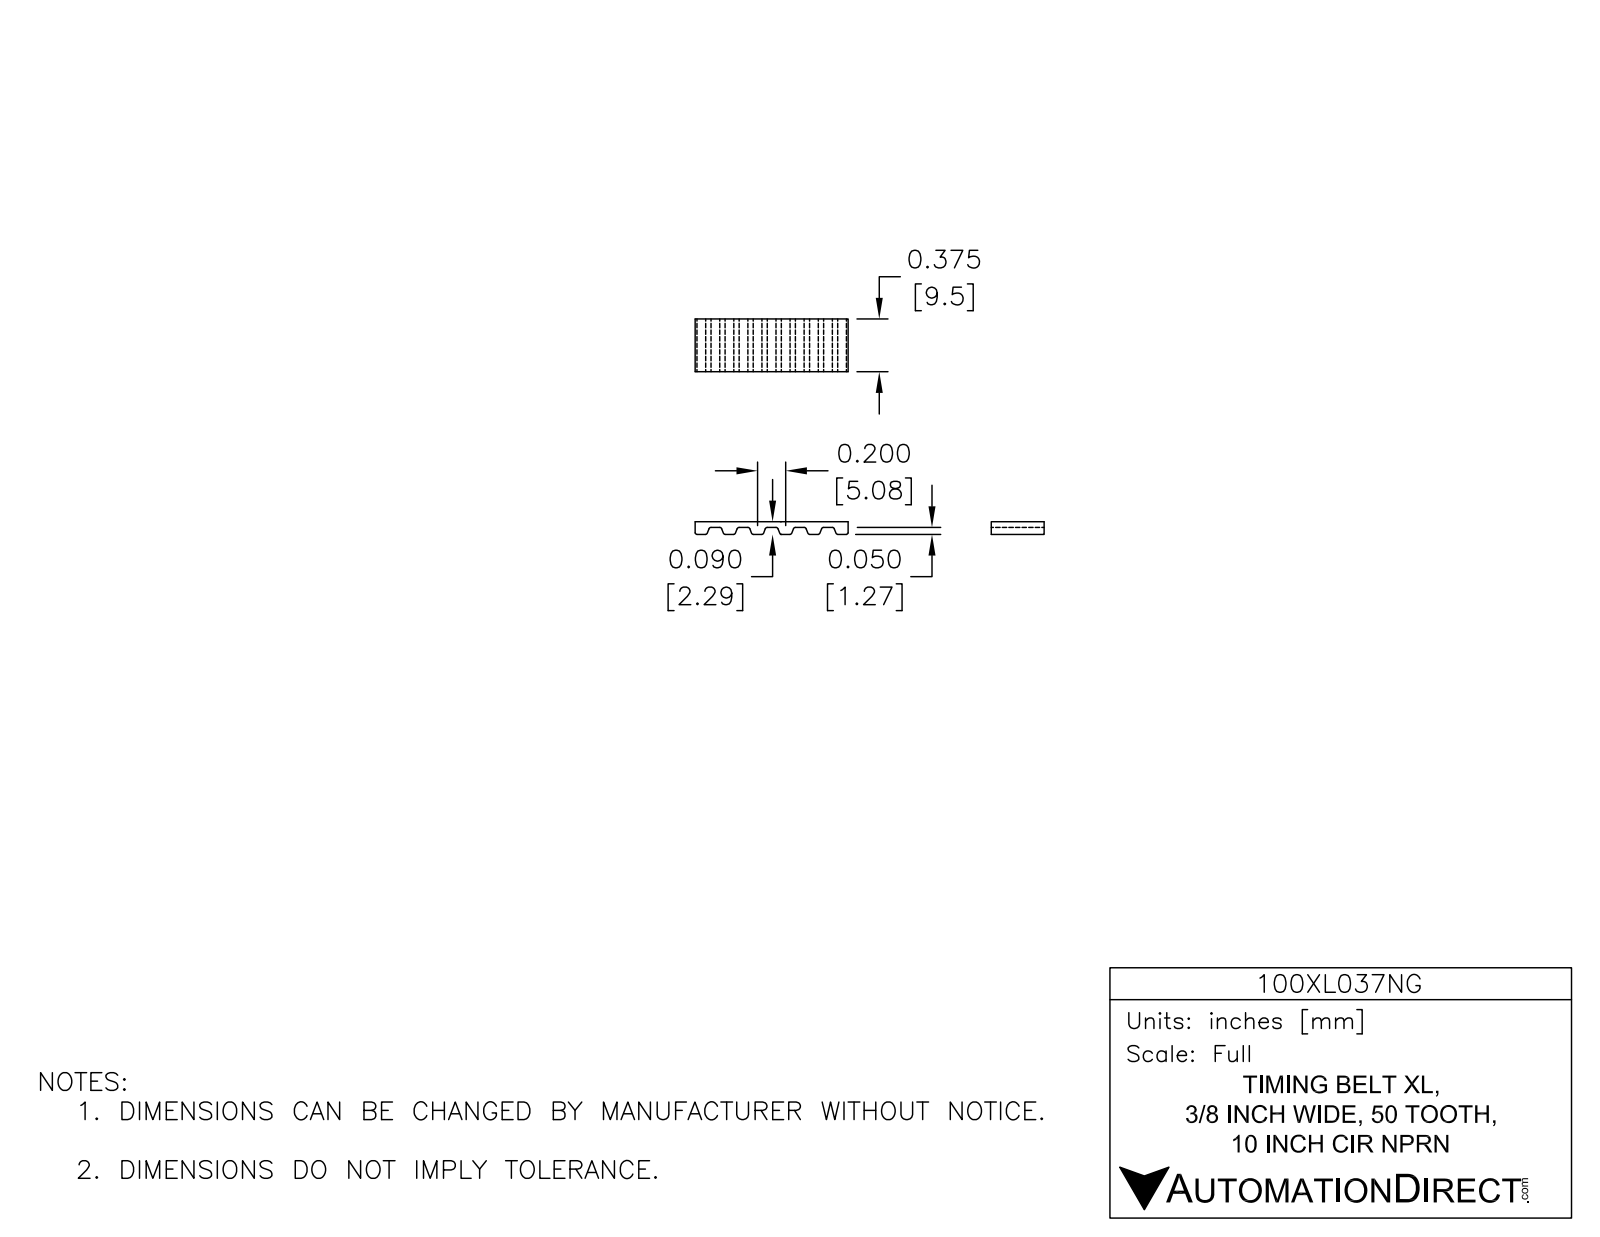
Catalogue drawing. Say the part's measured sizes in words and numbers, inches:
The part is named "100XL037NG". Its 3-D file was written by "SolidWorks 2014 (AUTOMOTIVE_DESIGN)". It is 1 solid with 441 faces: 158 planar, 283 cylindrical and 0 other. Overall it measures 3.288 by 3 by 0.375 inches. Its volume is 0.203 cubic inches and its surface area 9.521 square inches. Partial cylindrical surfaces (rounded edges, fillets, slot ends): 200 of radius 0.015, 2 of radius 1.46, 2 of radius 1.5. The main face-to-face distances are 0.375, 0.04, 2.96, 3, 2.92, 1.438, 1.426, 0.903, 1.448, 1.425.
